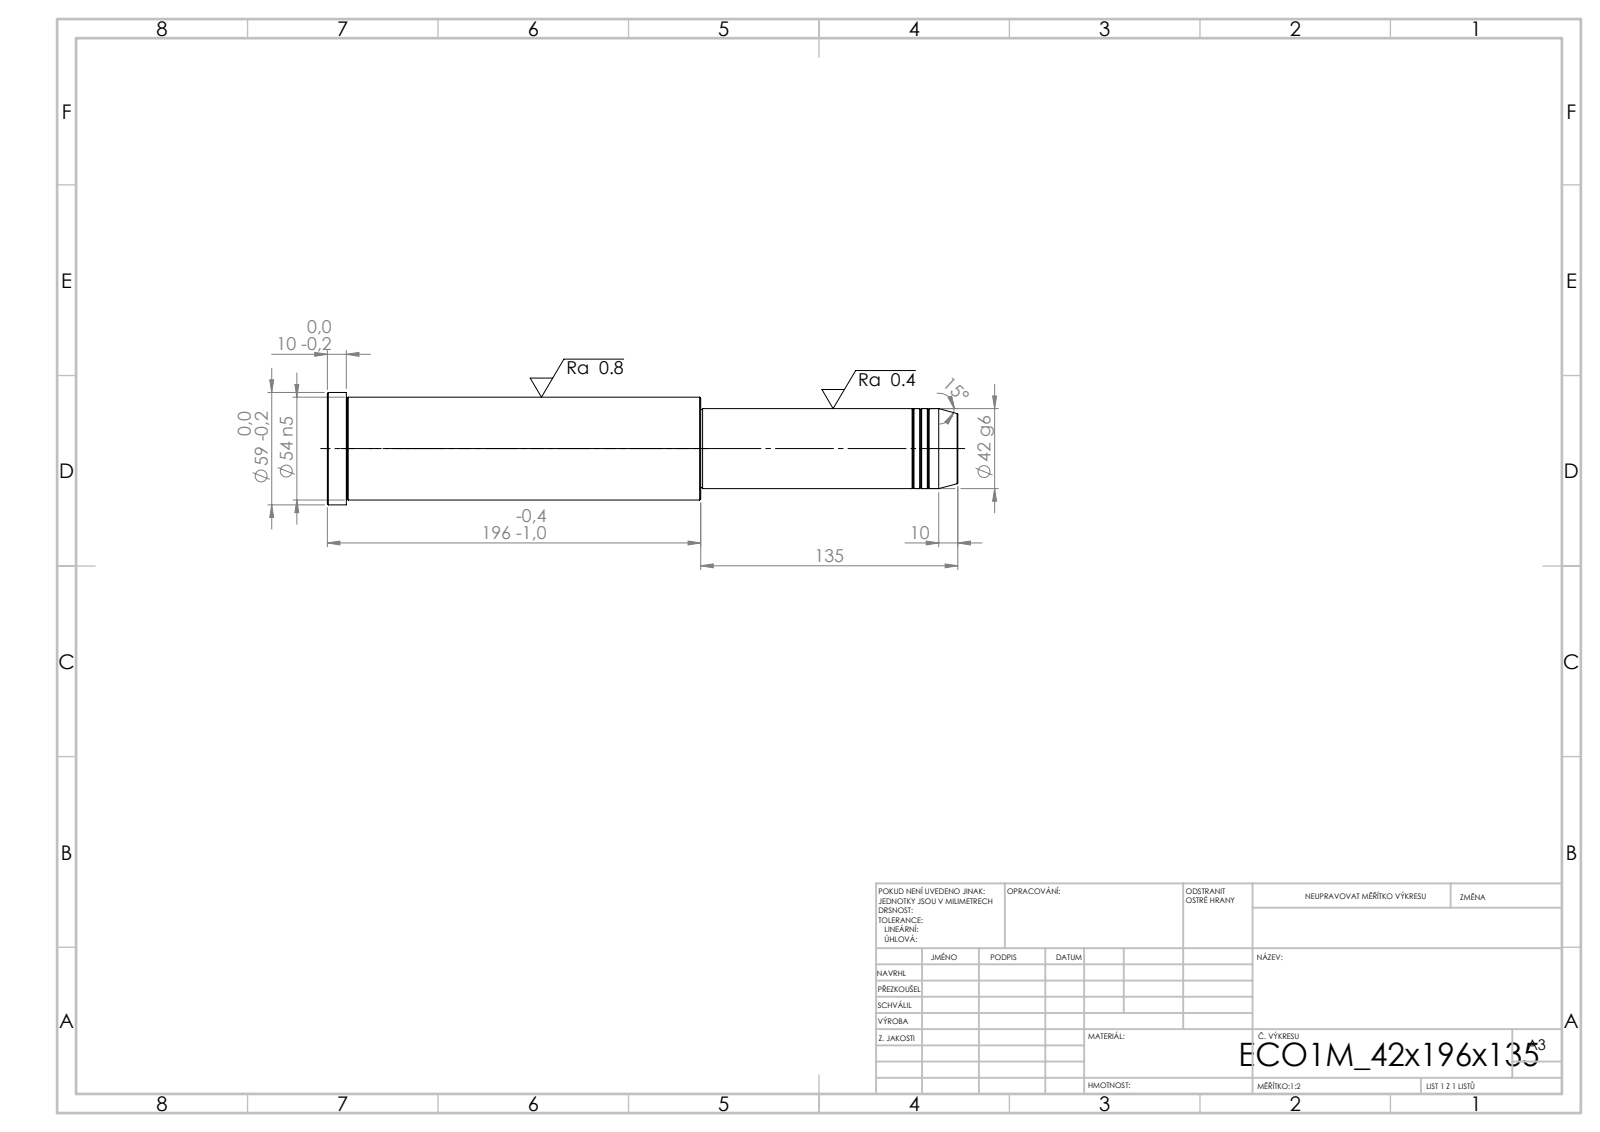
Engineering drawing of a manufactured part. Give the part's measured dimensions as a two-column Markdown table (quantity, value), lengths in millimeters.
| quantity | value |
| --- | --- |
| STEP written by | SolidWorks 2019 (CONFIG_CONTROL_DESIGN) |
| units | millimeters |
| bodies | 1 solid, 43 faces (5 planar, 14 cylindrical, 24 other) |
| overall size | 331 × 59 × 59 |
| volume | 638 330 mm³ |
| surface area | 56 637 mm² |
| round bosses / shafts (diameter × count) | 59 × 1, 54 × 1, 42 × 1, 41 × 1 |
| main face-to-face distances | 331, 135, 196, 321, 186, 10, 134, 1, 187, 197 |
